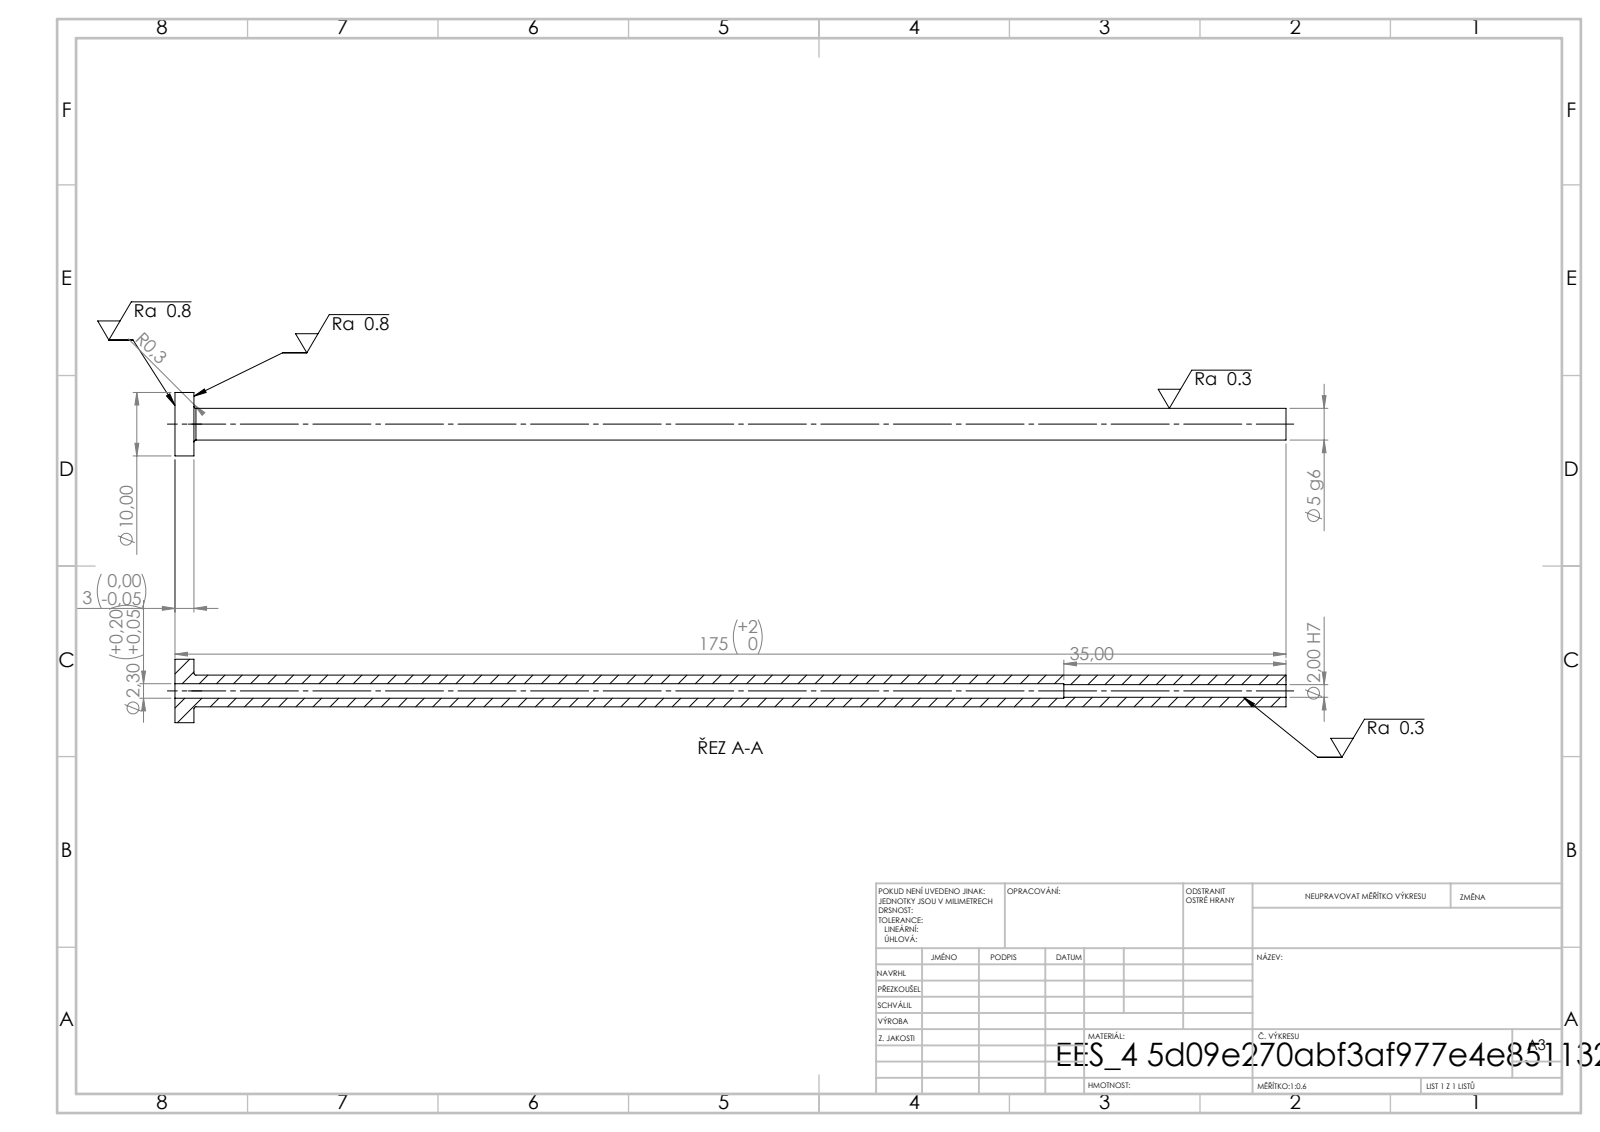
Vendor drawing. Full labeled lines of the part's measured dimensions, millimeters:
STEP written by: SolidWorks 2019 (CONFIG_CONTROL_DESIGN)
Units: millimetres
Bodies: 1 solid, 14 faces (4 planar, 8 cylindrical, 2 other)
Overall size (bounding box): 175 × 10 × 10
Volume: 2 922 mm³ · Surface area: 4 176 mm²
Round holes (diameter × count): ⌀2 ×1, ⌀2.3 ×1
Round bosses / shafts (diameter × count): ⌀10 ×1, ⌀5 ×1
Main face-to-face distances: 3, 175, 172, 140, 137, 35
